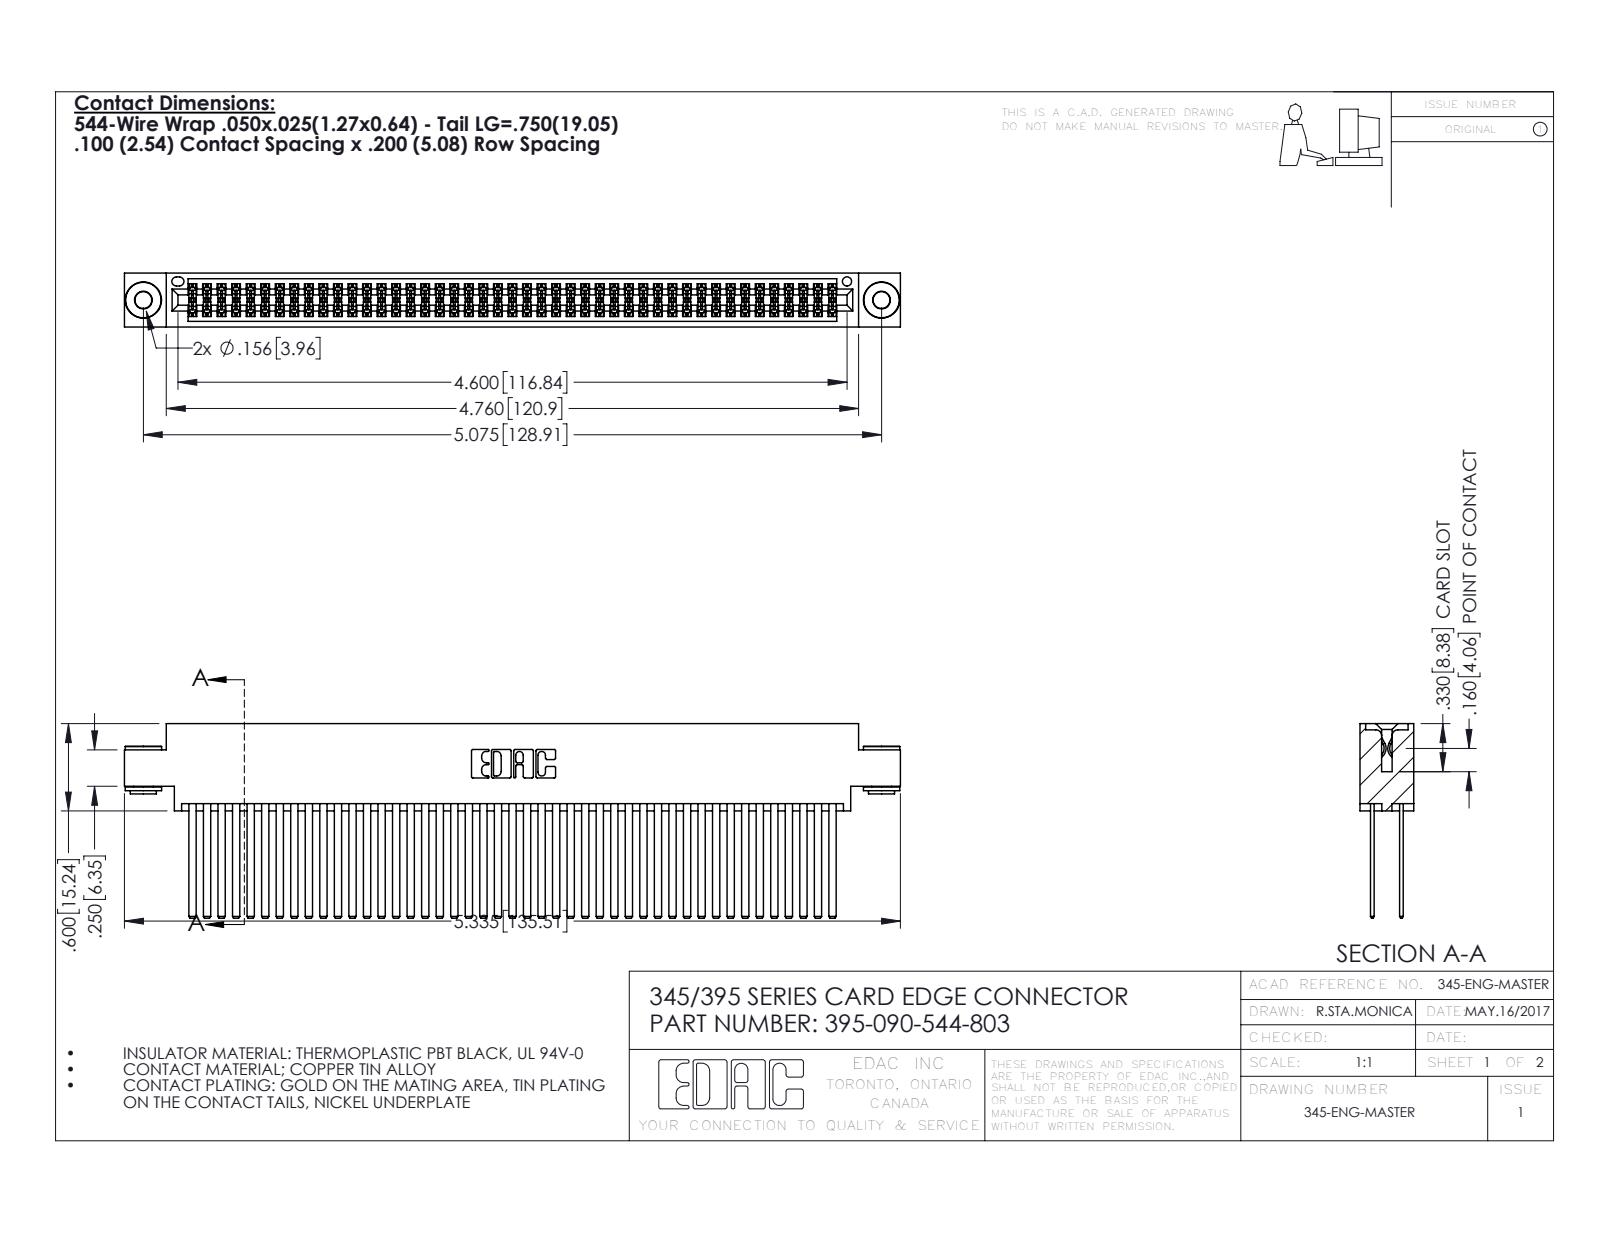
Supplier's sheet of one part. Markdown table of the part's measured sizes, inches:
| quantity | value |
| --- | --- |
| part name | 395-090-544-803; 345-292-001_345-293-144; 345-250-002_345-250-002-102; 345 Part_0.170 Offset - 0.156 Dia-TH |
| STEP written by | SolidWorks 2016 (CONFIG_CONTROL_DESIGN) |
| units | inches |
| bodies | 93 solids, 4128 faces (2704 planar, 1416 cylindrical, 8 other) |
| overall size | 5.335 × 1.337 × 0.37 |
| volume | 0.876 in³ |
| surface area | 39.26 in² |
| round holes (diameter × count) | 0.116 × 2, 0.156 × 2, 0.064 × 1 |
| round bosses / shafts (diameter × count) | 0.25 × 2, 0.18 × 2, 0.136 × 2 |
| partial cylindrical surfaces (radius × count) | 0.006 × 135, 0.01 × 22, 0.007 × 6, 0.031 × 6, 0.026 × 3, 0.014 × 2, 0.019 × 2, 0.022 × 2 |
| main face-to-face distances | 0.2, 0.025, 0.072, 0.098, 0.272, 0.298, 0.225, 0.175, 0.37, 0.15 |
| hole center spacings | 0.27, 4.839, 5.075 |
